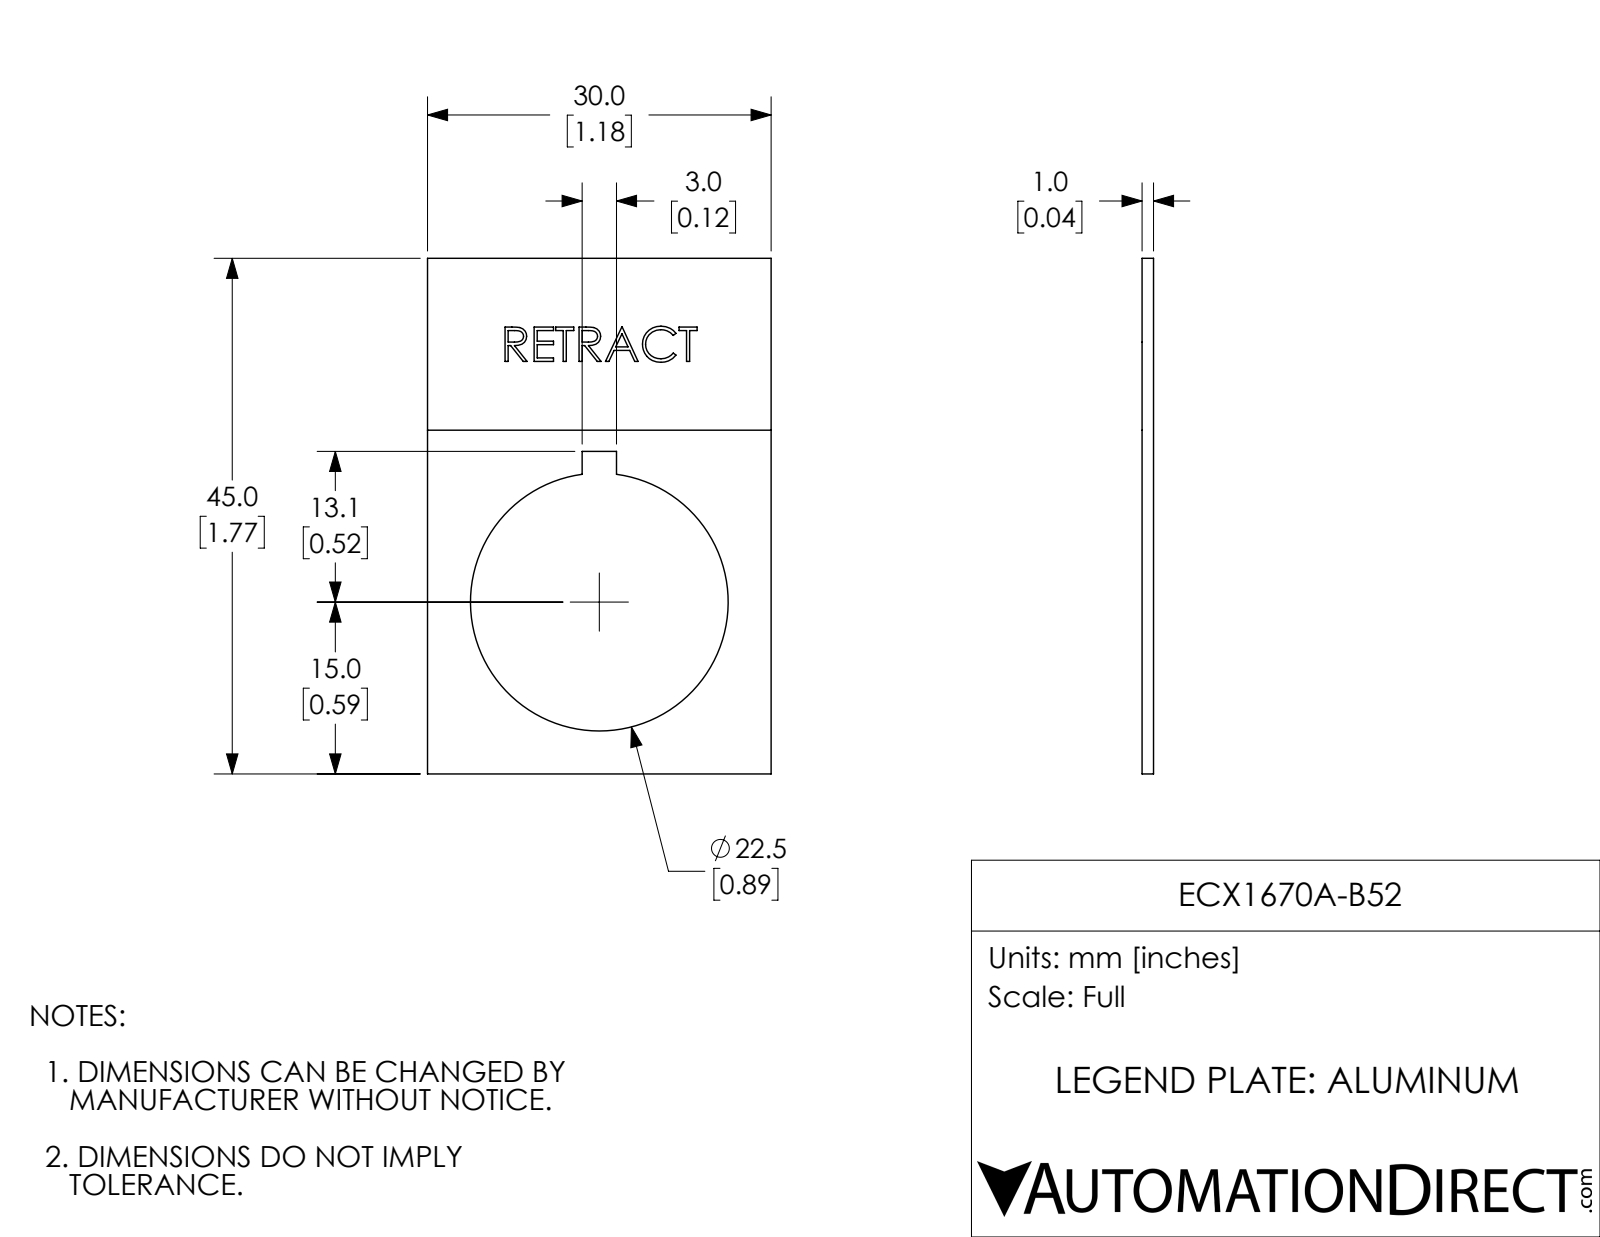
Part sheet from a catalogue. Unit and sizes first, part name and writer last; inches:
Units: inches
Overall size (bounding box): 1.772 × 1.181 × 0.039
Round holes (diameter × count): ⌀0.886 ×1
Main face-to-face distances: 0.039, 1.181, 1.772, 0.038, 0.65, 0.531, 1.108, 0.663, 0.118, 0.1
Volume: 0.058 in³ · Surface area: 3.287 in²
Bodies: 1 solid, 105 faces (83 planar, 3 cylindrical, 19 other)
Part name (STEP PRODUCT): ECX1670A-B52
STEP written by: SolidWorks 2017 (AUTOMOTIVE_DESIGN)
